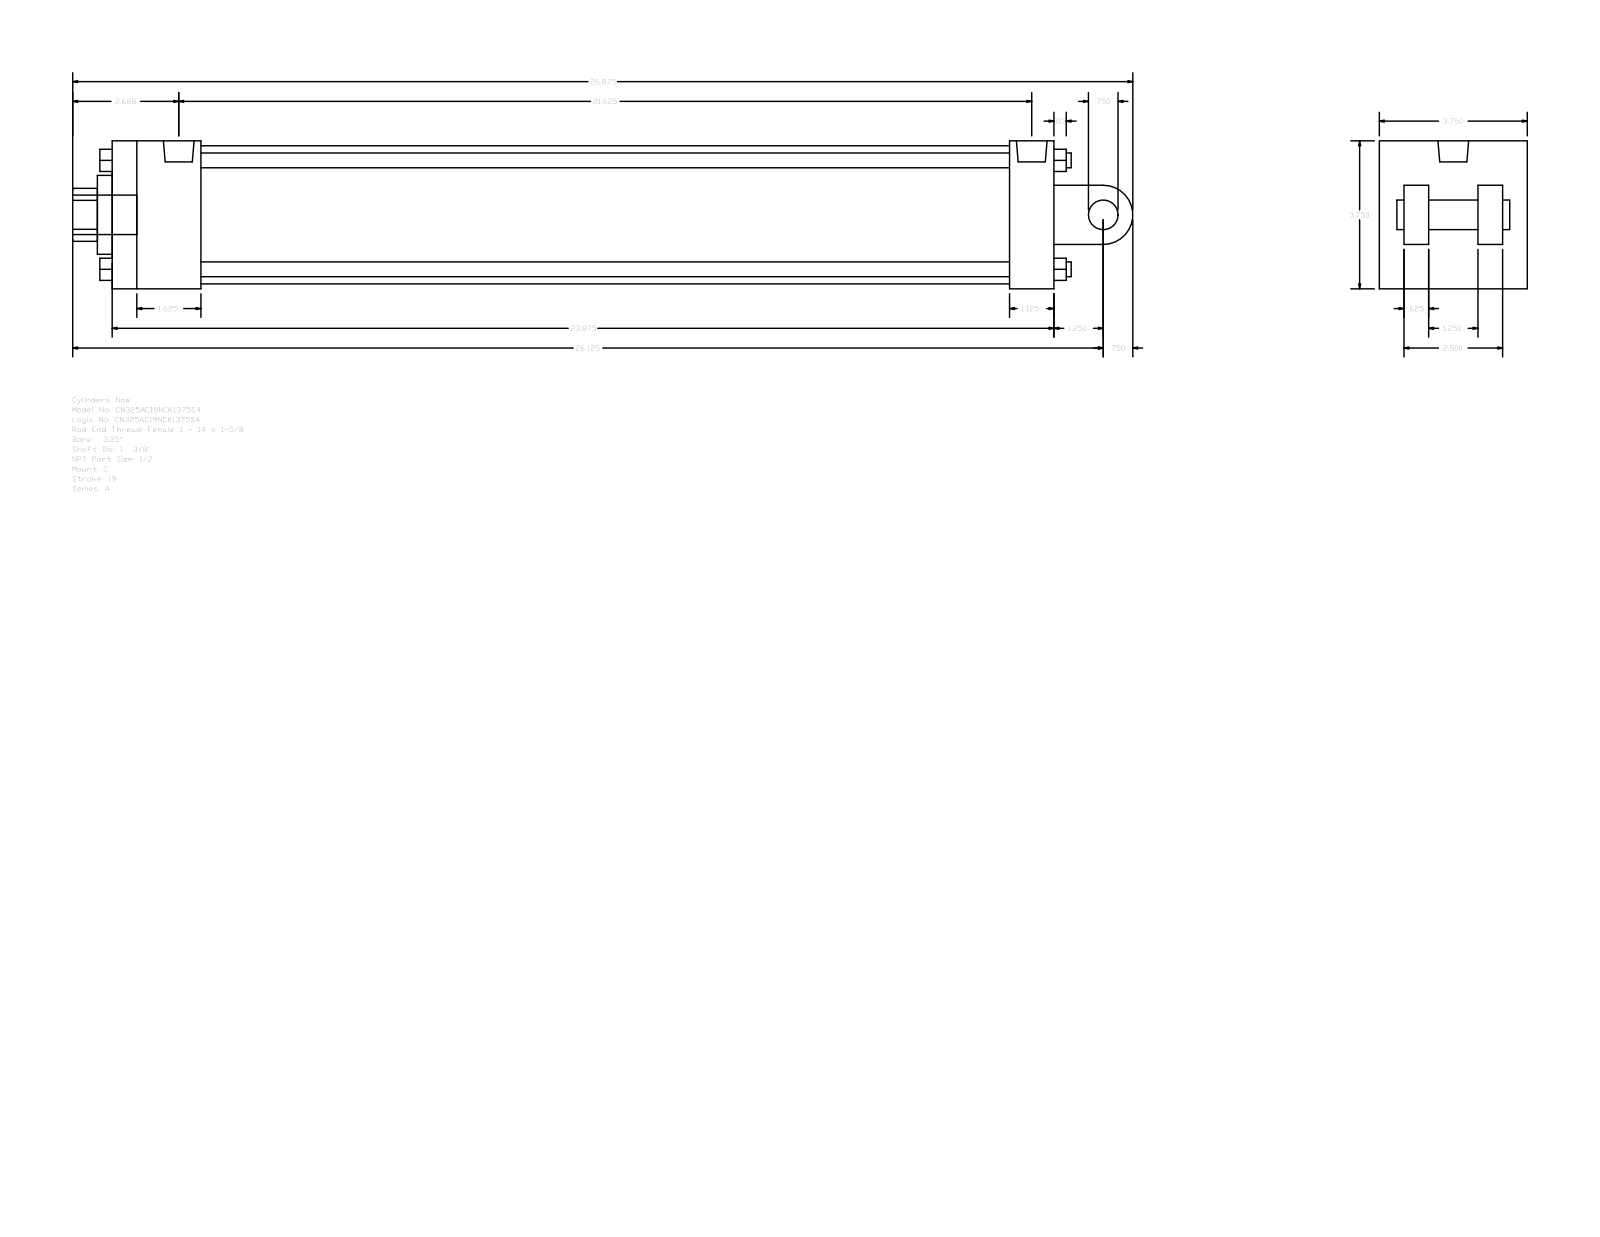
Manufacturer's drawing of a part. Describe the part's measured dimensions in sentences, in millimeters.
The part is named "A_C__0325_1.375". Its 3-D file was written by "GSSL Pune (CONFIG_CONTROL_DESIGN)". It is 0 solids with 135 faces: 102 planar, 33 cylindrical and 0 other. Overall it measures 682.62 by 95.25 by 95.25 millimeters. Round holes: 2 of diameter 8.73, 1 of diameter 19.77, 1 of diameter 34.92, 1 of diameter 50.8, 1 of diameter 88.9. Round bosses or shafts: 4 of diameter 9.53, 2 of diameter 8.73, 1 of diameter 25.4, 1 of diameter 19.77, 1 of diameter 19.05. Partial cylindrical surfaces (rounded edges, fillets, slot ends): 1 of radius 17.06, 1 of radius 19.05. The main face-to-face distances are 95.24, 15.87, 606.43, 63.5, 66.67, 28.58, 31.74, 79.37, 47.63, 577.85. The hole center spacings are 3.18.
